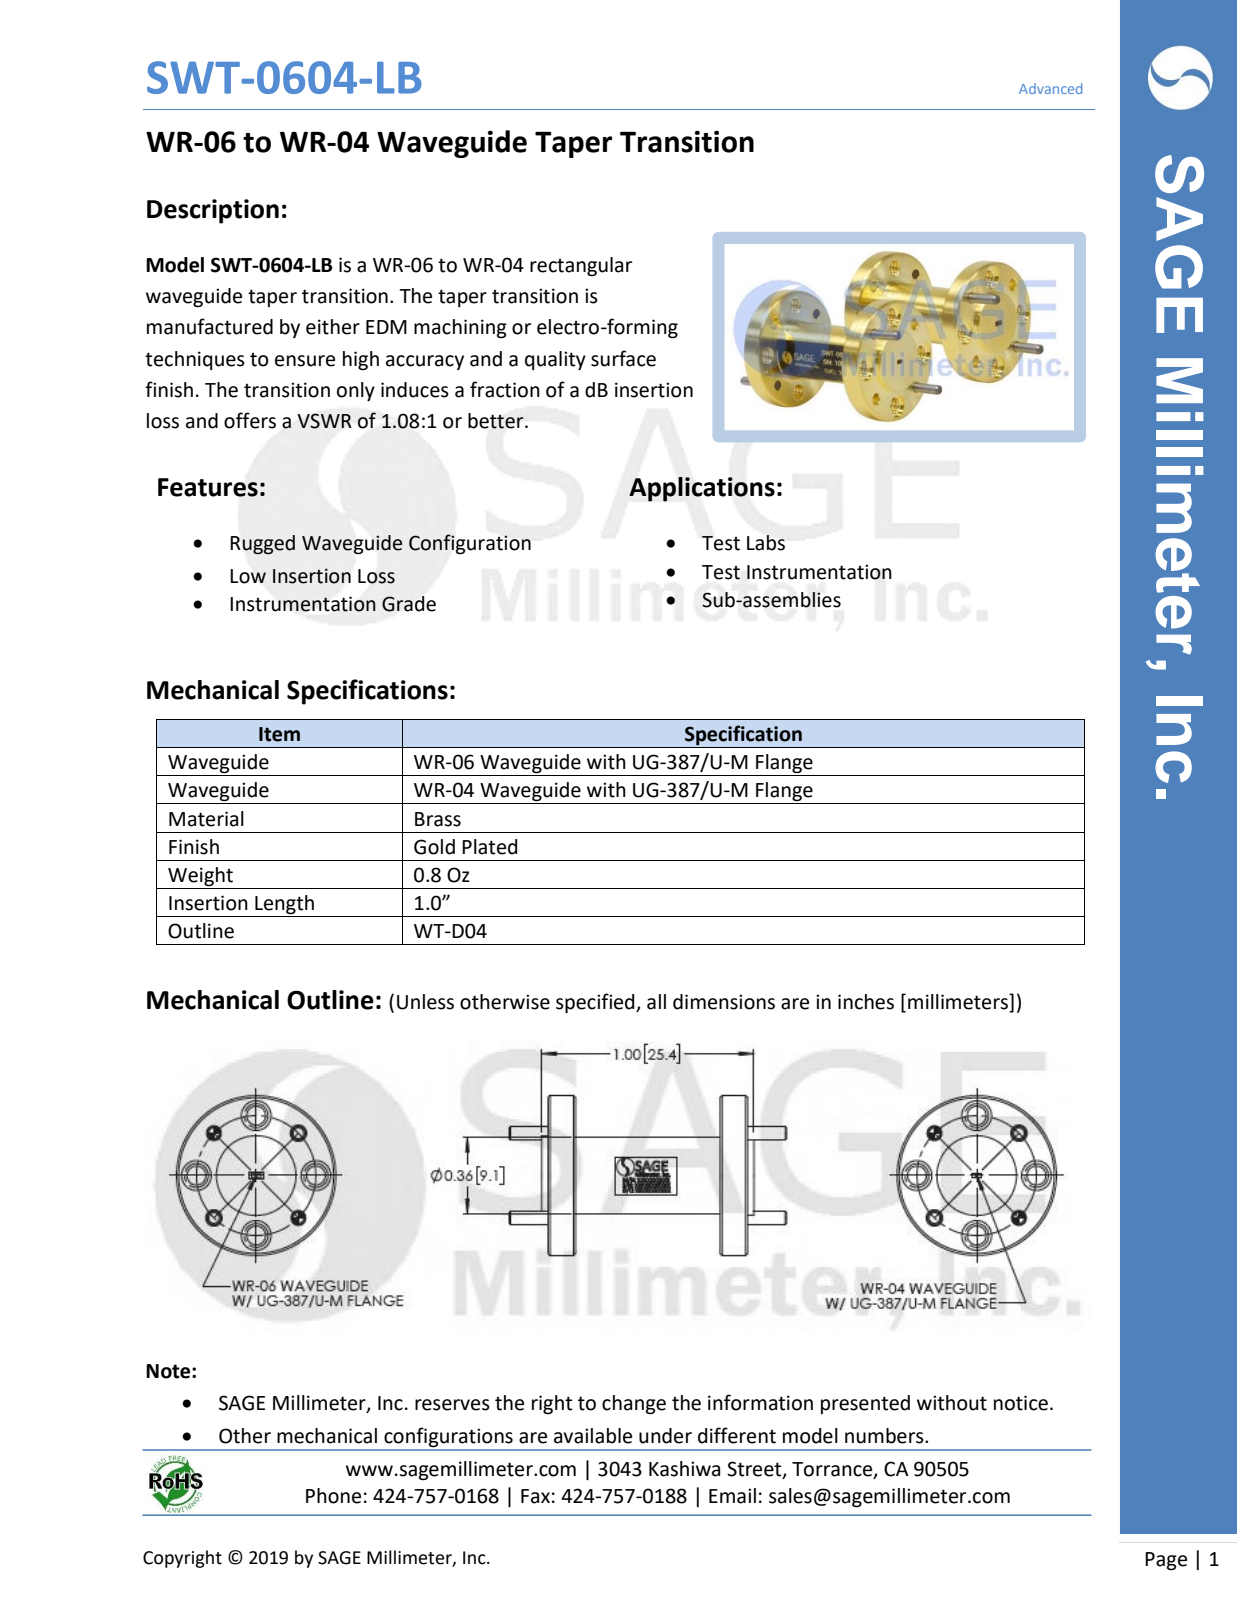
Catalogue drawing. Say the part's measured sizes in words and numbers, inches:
The part is named "SWT-0604-LB". Its 3-D file was written by "SolidWorks 2021 (CONFIG_CONTROL_DESIGN)". It is 5 solids with 148 faces: 34 planar, 74 cylindrical and 40 other. Overall it measures 1.305 by 0.75 by 0.75 inches. Its volume is 0.19 cubic inches and its surface area 3.866 square inches. Round holes: 4 of diameter 0.061, 4 of diameter 0.067, 4 of diameter 0.089, 4 of diameter 0.14, 1 of diameter 0.68. Round bosses or shafts: 4 of diameter 0.063, 1 of diameter 0.75, 1 of diameter 0.375, 1 of diameter 0.36. The main face-to-face distances are 0.14, 0.82, 0.68, 0.96, 0.02, 0.16, 0.84, 0.98, 0.98, 1. The hole center spacings are 0.215, 0.398, 0.52, 0.281, 0.281, 0.563, 0.398, 0.519.
